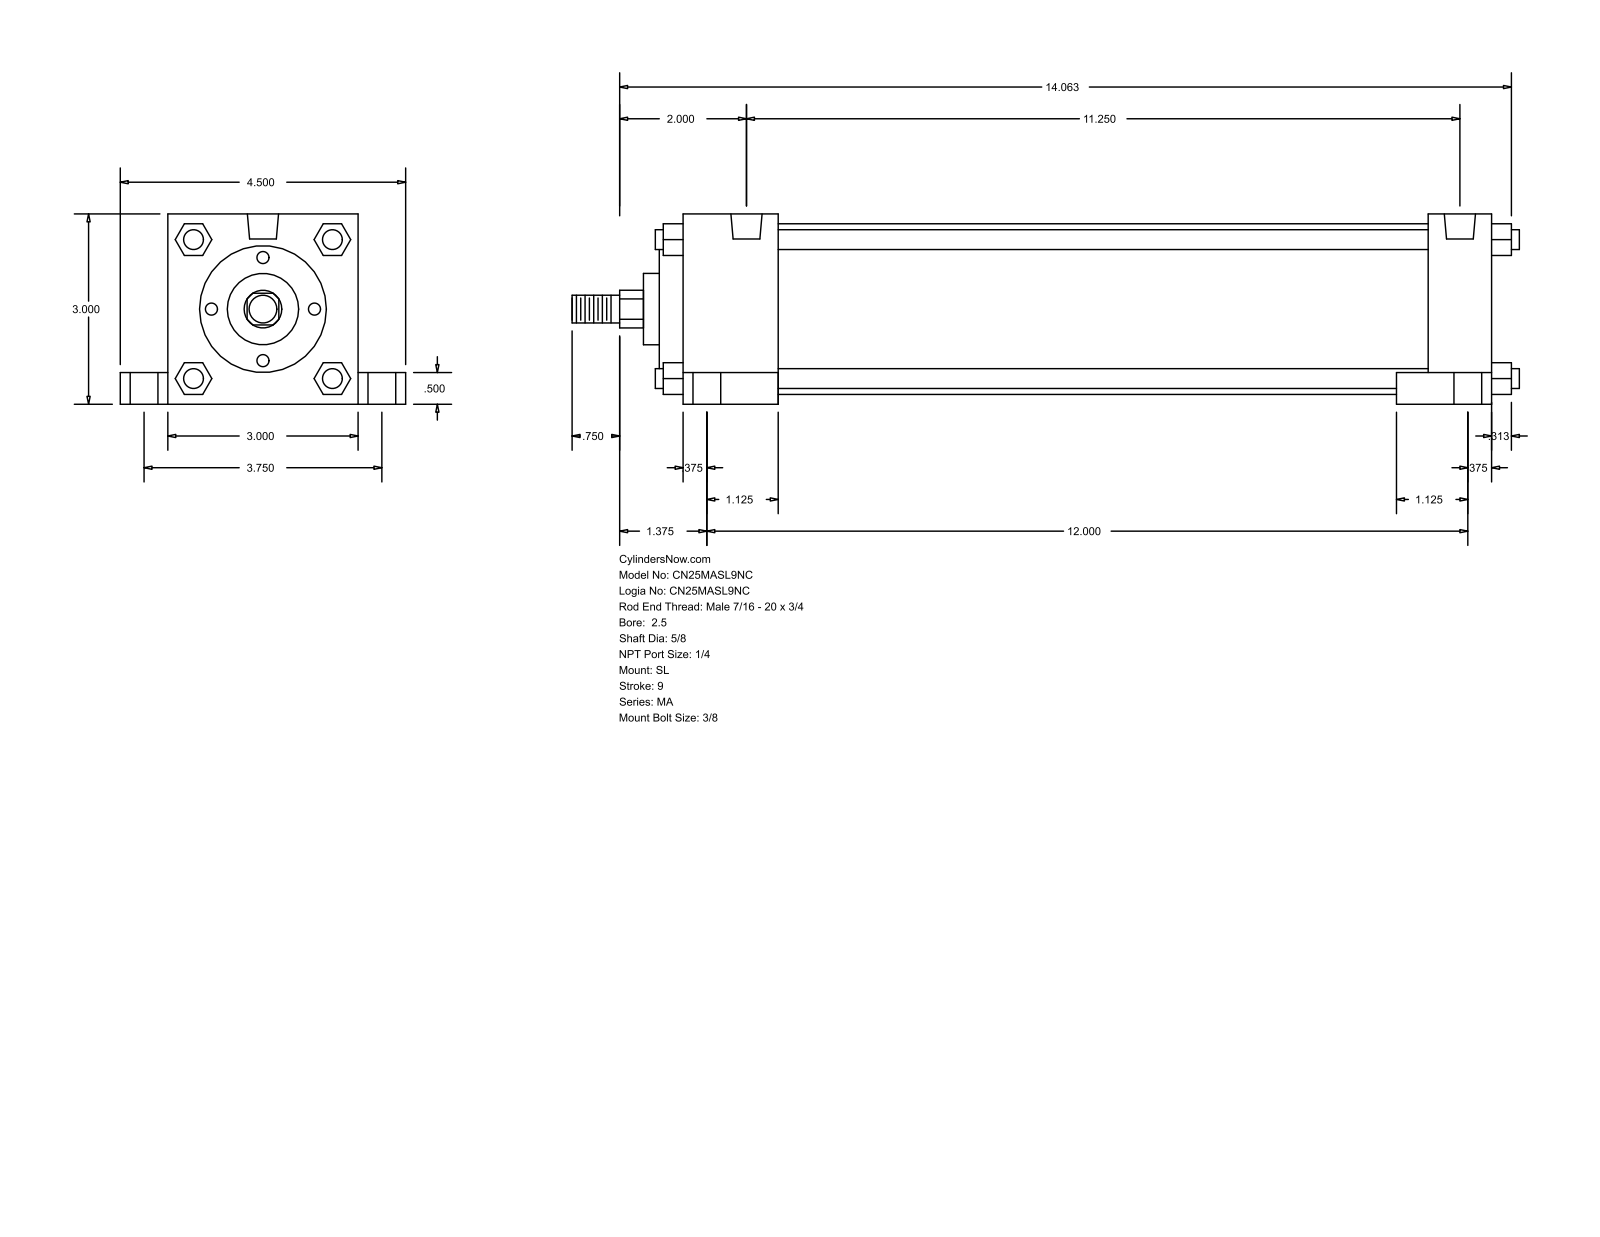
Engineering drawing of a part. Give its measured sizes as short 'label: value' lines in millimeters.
name: MA_SL__0250_0.625
written by: GSSL Pune (CONFIG_CONTROL_DESIGN)
unit: mm
bodies: 0 solids, 150 faces (113 planar, 37 cylindrical, 0 other)
size: 379.41 × 114.3 × 76.2
holes: 4× ⌀7.94, 4× ⌀11.11, 4× ⌀17.46, 2× ⌀12.49
bosses: 4× ⌀7.94, 1× ⌀68.33, 1× ⌀50.8, 1× ⌀28.57, 1× ⌀15.88, 1× ⌀11.11
rounds: 1× R7.54
face distances: 76.2, 323.85, 12.7, 260.35, 25.4, 38.1, 285.75, 298.45, 19.05, 63.5
hole spacings: 47.73, 50.2, 95.24, 285.75, 292.83, 304.81, 305.37, 319.34
